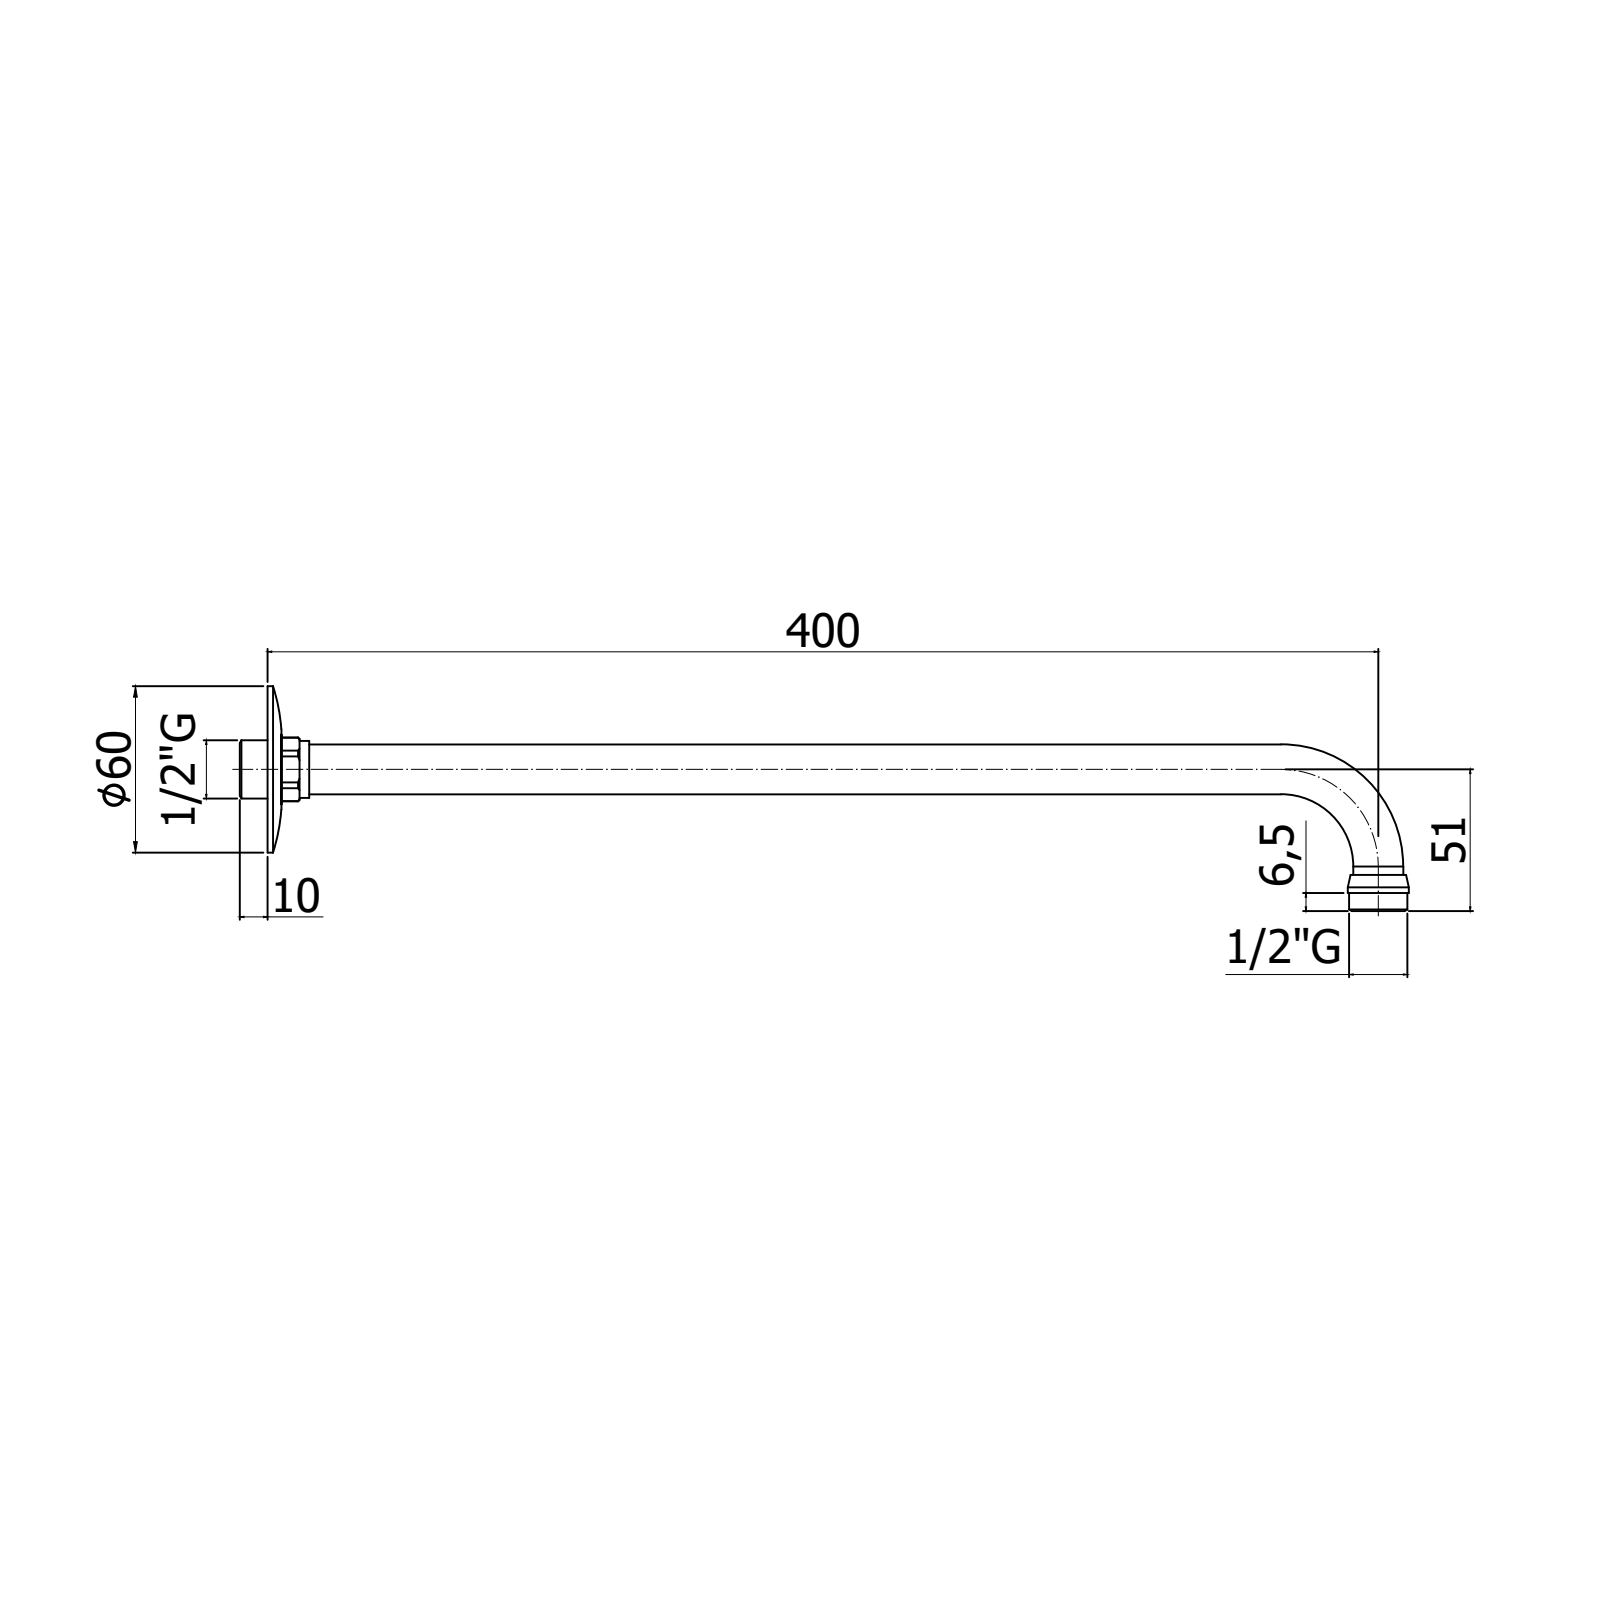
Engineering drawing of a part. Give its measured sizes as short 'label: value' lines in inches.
name: ZSOF017CR
written by: CREO PARAMETRIC BY PTC INC, 2020044 (CONFIG_CONTROL_DESIGN)
unit: in
bodies: 1 solid, 88 faces (24 planar, 26 cylindrical, 38 other)
size: 16.181 × 3.15 × 2.283
volume: 1.077 in³; area: 84.44 in²
holes: 2× ⌀0.591, 1× ⌀0.669, 1× ⌀2.244
bosses: 2× ⌀0.827, 1× ⌀2.283, 1× ⌀0.866, 1× ⌀0.709
rounds: 1× R0.453
face distances: 0.157, 0.827, 0.177, 0.02, 0.591, 0.433, 0.413, 0.512, 0.315, 0.138
